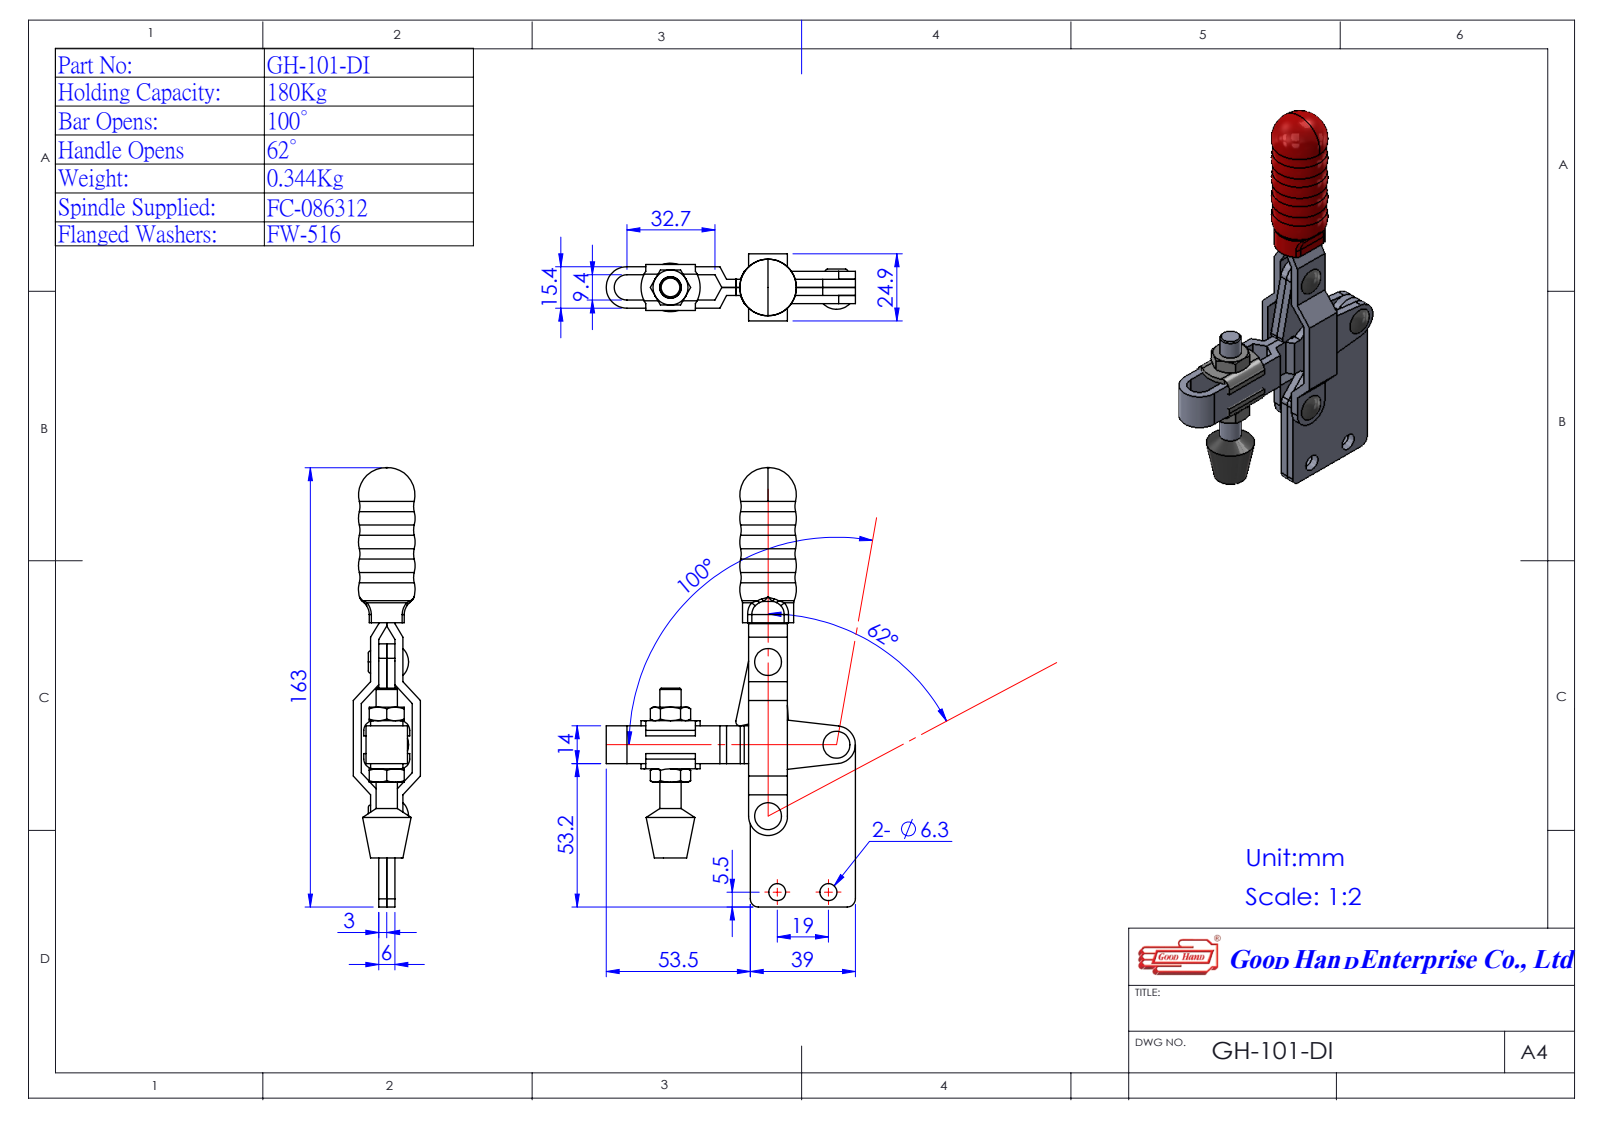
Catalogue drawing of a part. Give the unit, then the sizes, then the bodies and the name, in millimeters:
Units: millimetres
Overall size (bounding box): 163.01 × 92.5 × 24.9
Round holes (diameter × count): ⌀5 ×4, ⌀6.3 ×2
Round bosses / shafts (diameter × count): ⌀6.3 ×4, ⌀7.93 ×1
Partial cylindrical surfaces — rounded edges, fillets, slot ends (radius × count): R0.5 ×4, R1.2 ×4, R2 ×4, R3 ×4, R3.6 ×4, R6 ×2, R6.75 ×2, R11.04 ×2
Main face-to-face distances: 3, 6, 1.7, 10.7, 9, 4.75, 6.45, 15.45, 17.15, 4.7
Hole centre spacings: 19, 24.2, 26.53, 28.4, 30.72, 36.01, 36.71, 39.85
Volume: 57 966 mm³ · Surface area: 29 487 mm²
Bodies: 5 solids, 336 faces (138 planar, 100 cylindrical, 98 other)
Part name (STEP PRODUCT): GH-101-DI(簡化)-1; Group6^GH-101-DI(簡化)-1; Group3^GH-101-DI(簡化)-1; Group4^GH-101-DI(簡化)-1 (+2 more)
STEP written by: SolidWorks 2016 (AUTOMOTIVE_DESIGN)
